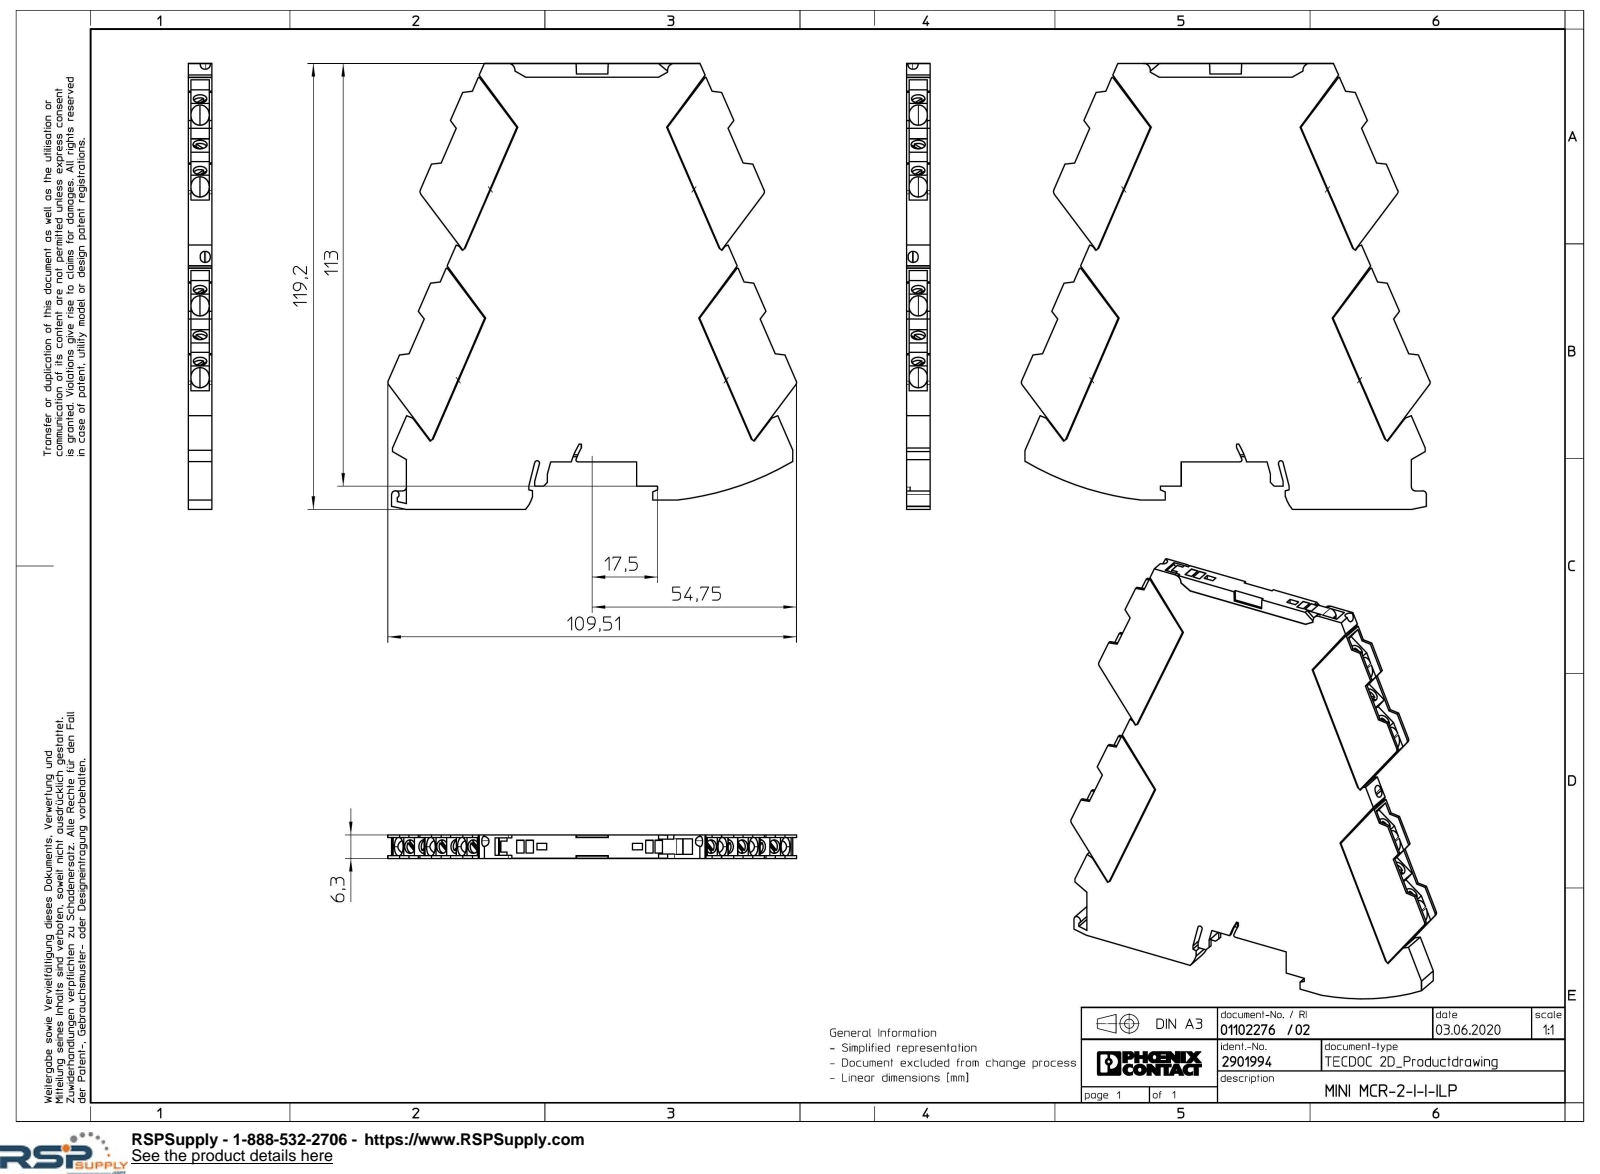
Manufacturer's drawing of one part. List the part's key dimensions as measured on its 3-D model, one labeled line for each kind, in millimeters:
Part name (STEP PRODUCT): FASTCON_PRO-SET-select.1; MINI_ANALOG_PRO-SOCKEL-select; MINI_ANALOG_PRO-SC-select
STEP written by: Creo Elements/Direct Modeling 20.1A 29-Sep-2018 (C) Parametric Technology GmbH (AUTOMOTIVE_DESIGN)
Units: millimetres
Bodies: 5 solids, 1290 faces (1152 planar, 125 cylindrical, 13 other)
Overall size (bounding box): 119.2 × 109.51 × 6.3
Volume: 58 180 mm³ · Surface area: 35 865 mm²
Round holes (diameter × count): ⌀3.6 ×8, ⌀3.3 ×4, ⌀3.8 ×4
Round bosses / shafts (diameter × count): ⌀3 ×4
Partial cylindrical surfaces — rounded edges, fillets, slot ends (radius × count): R2.4 ×32, R1 ×6, R0.2 ×5, R1.15 ×4, R1.18 ×4, R1.8 ×3, R0.5 ×1, R0.65 ×1
Main face-to-face distances: 6.3, 0.95, 4.4, 0.7, 5.35, 37.57, 5.03, 5.6, 1.95, 0.31
Hole centre spacings: 37.56, 7.28, 10.92, 18.2, 26.64, 44.84, 19.36, 30.28
